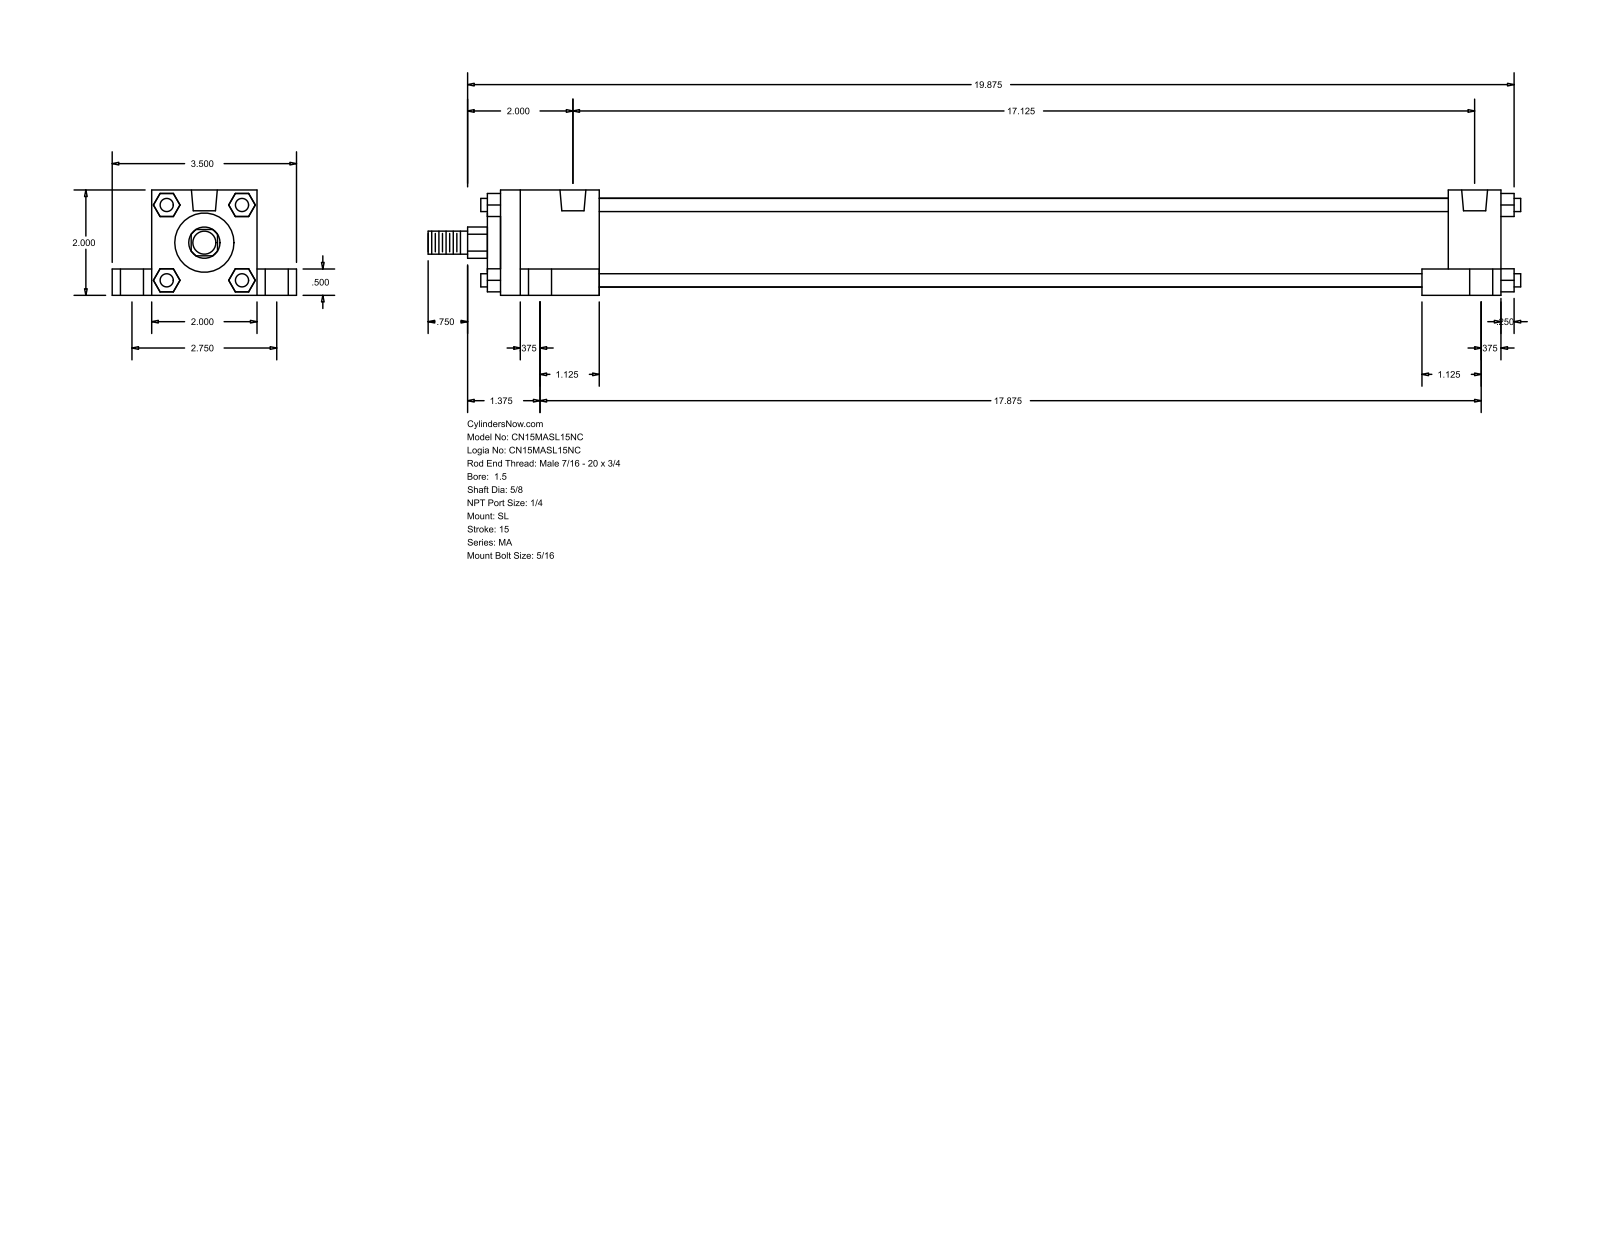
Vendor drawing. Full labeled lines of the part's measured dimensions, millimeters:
Part name (STEP PRODUCT): MA_SL__0150_0.625
STEP written by: GSSL Pune (CONFIG_CONTROL_DESIGN)
Units: millimetres
Bodies: 0 solids, 148 faces (112 planar, 36 cylindrical, 0 other)
Overall size (bounding box): 527.05 × 88.9 × 50.8
Round holes (diameter × count): ⌀7.94 ×4, ⌀11.11 ×4, ⌀17.46 ×4, ⌀12.49 ×2
Round bosses / shafts (diameter × count): ⌀6.35 ×4, ⌀42.93 ×1, ⌀28.57 ×1, ⌀15.88 ×1, ⌀11.11 ×1
Partial cylindrical surfaces — rounded edges, fillets, slot ends (radius × count): R7.54 ×1
Main face-to-face distances: 50.8, 19.05, 38.1, 482.6, 69.85, 12.7, 409.57, 9.52, 457.19, 25.41
Hole centre spacings: 35.06, 38.36, 69.84, 434.97, 439.54, 452.2, 454.03, 459.37
